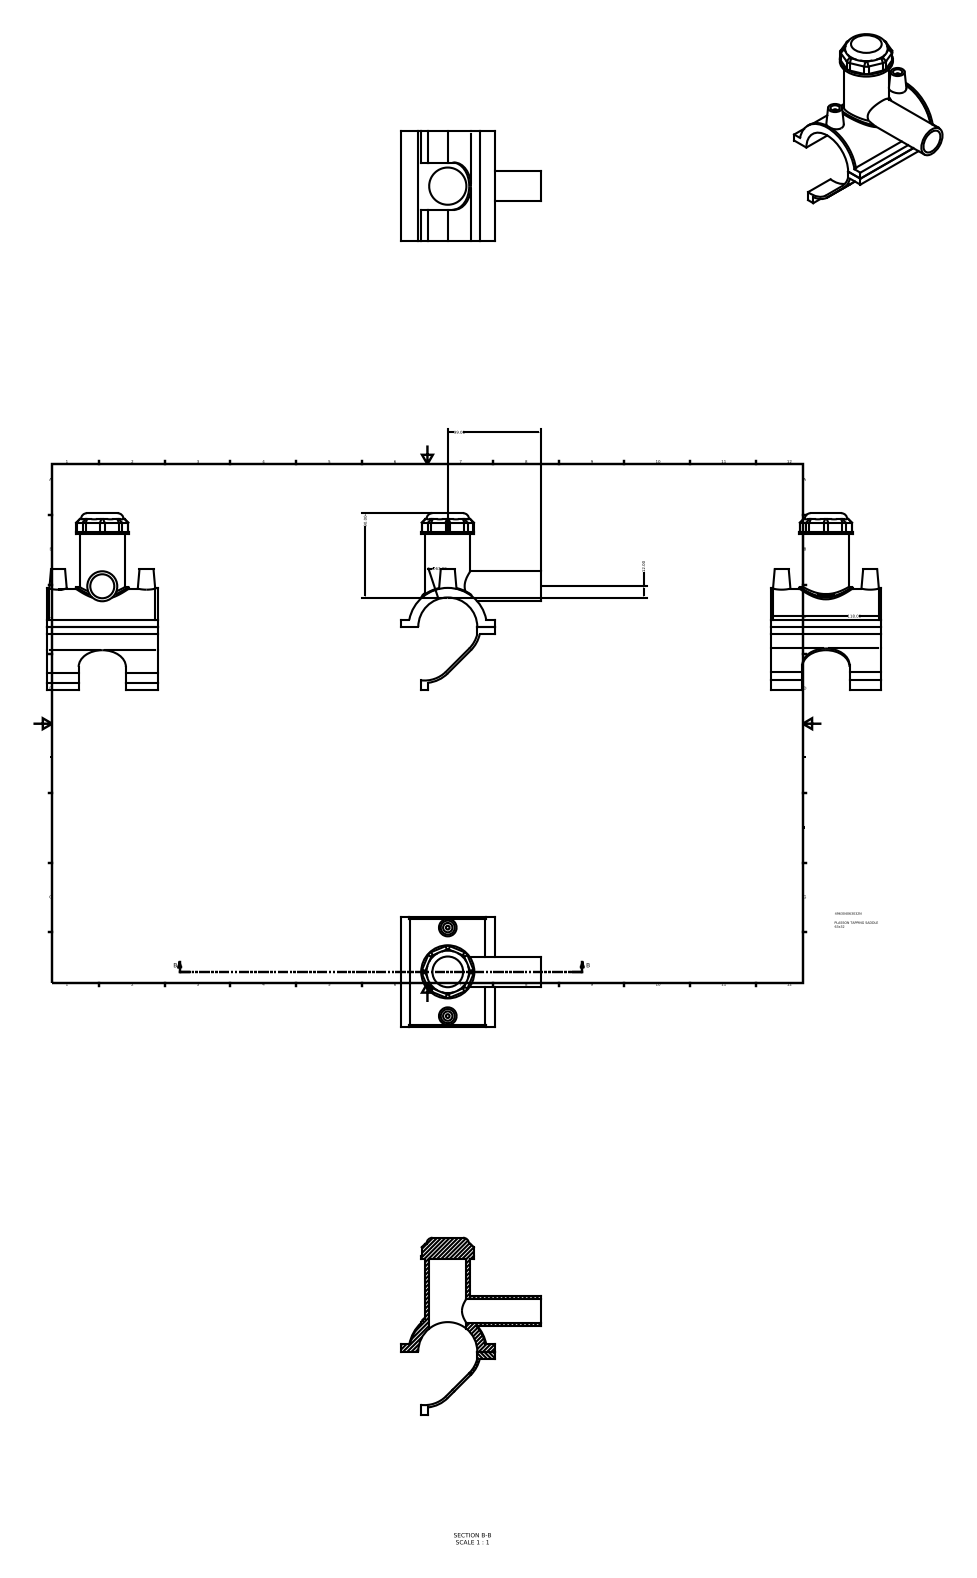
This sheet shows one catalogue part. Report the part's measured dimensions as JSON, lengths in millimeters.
{"part_name": "496304063032N", "step_written_by": "Autodesk Inventor 2015 (AUTOMOTIVE_DESIGN)", "units": "millimeters", "bodies": {"solids": 2, "faces": 108, "planar": 64, "cylindrical": 31, "other": 13}, "overall_size": [188.78, 149, 118], "volume_mm3": 280671, "surface_area_mm2": 97216, "round_holes": [[10, 2], [25.6, 1], [39.69, 1]], "round_bosses_or_shafts": [[4, 2], [56.7, 1], [48.2, 1], [32, 1]], "partial_cylinders_radius": [[6.3, 8], [32.38, 2], [34.98, 2], [25.2, 1], [26.93, 1], [31.5, 1], [40.95, 1], [41.77, 1]], "face_to_face_distances": [7.82, 2.6, 98.95, 106.77, 118, 7.83, 15.65, 91.12, 15.64, 91.13], "hole_center_spacings": [47.2, 94.4]}
